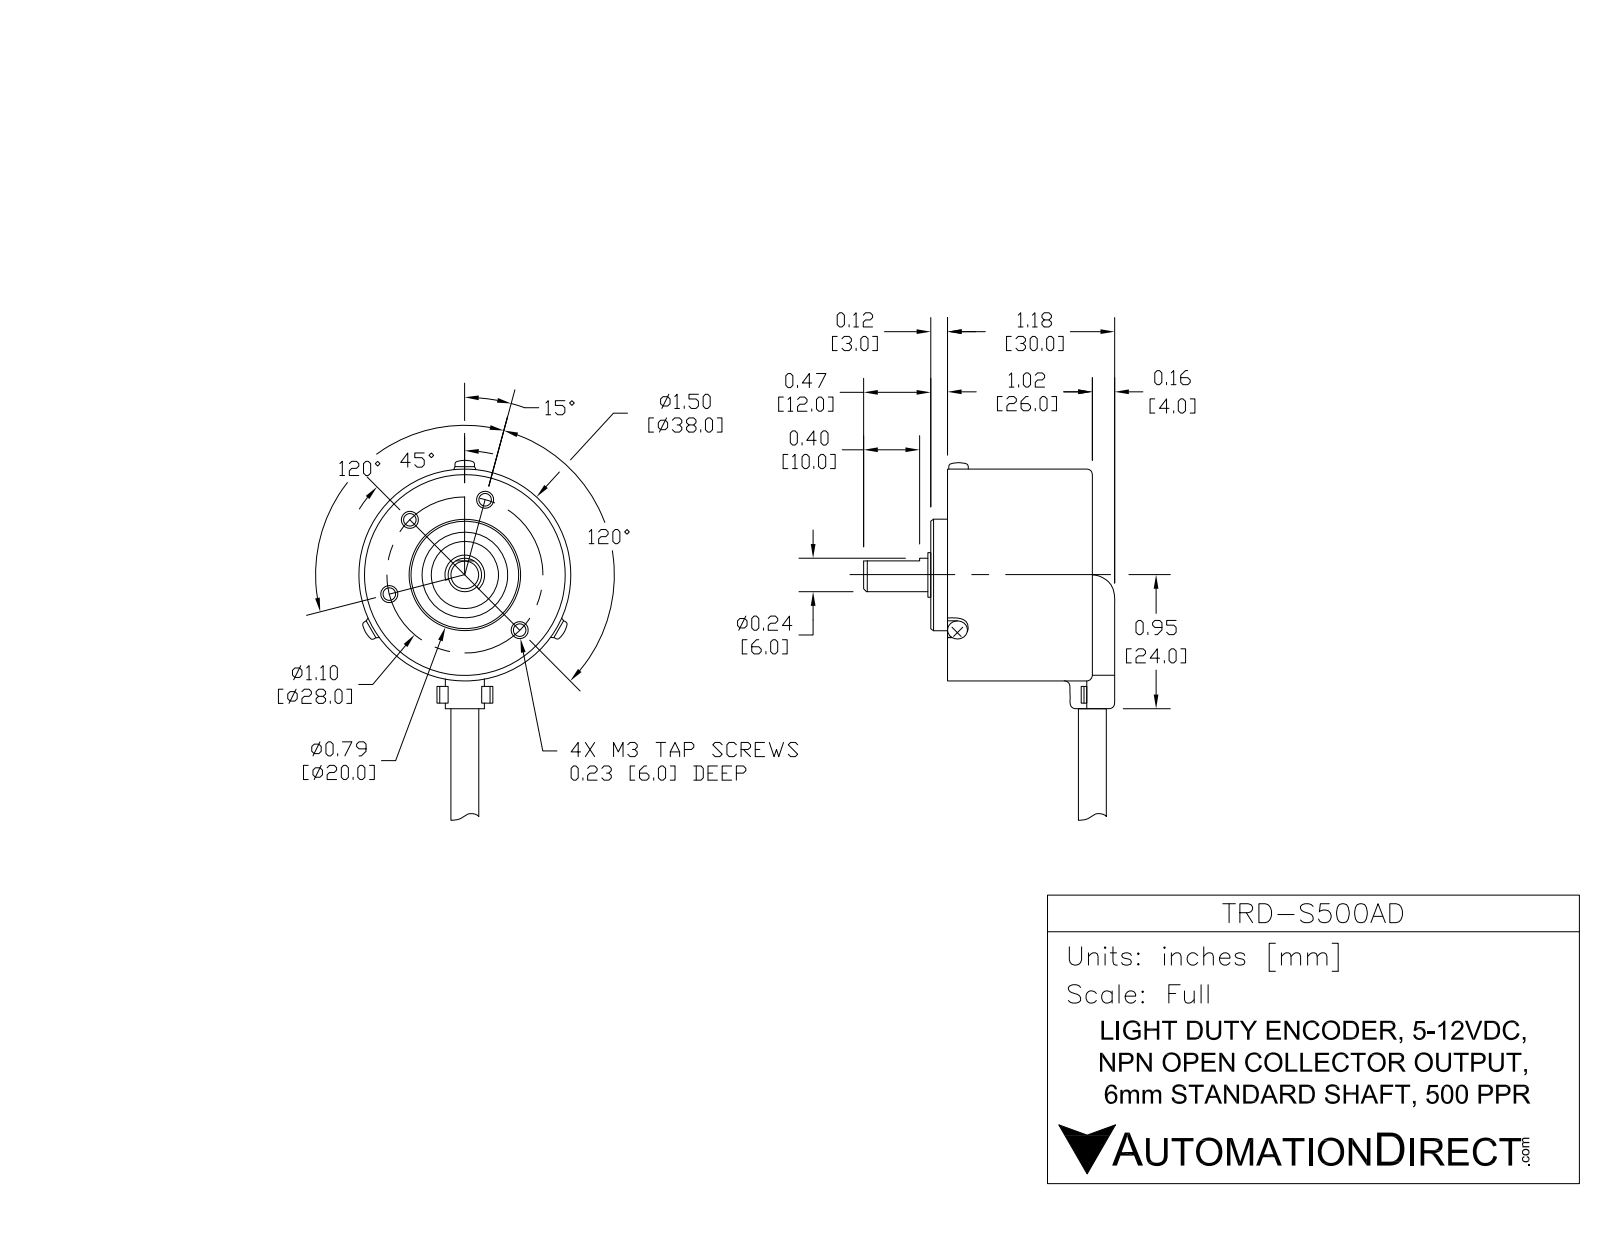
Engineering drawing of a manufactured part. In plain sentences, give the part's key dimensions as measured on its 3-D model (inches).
The part is named "TRD-S500AD". Its 3-D file was written by "SolidWorks 2016 (AUTOMOTIVE_DESIGN)". It is 3 solids with 257 faces: 98 planar, 100 cylindrical and 59 other. Overall it measures 7.189 by 1.768 by 1.496 inches. Its volume is 2.068 cubic inches and its surface area 13.85 square inches. Round holes: 4 of diameter 0.118, 1 of diameter 0.205, 1 of diameter 0.256, 1 of diameter 1.409. Round bosses or shafts: 1 of diameter 1.496, 1 of diameter 0.787, 1 of diameter 0.591, 1 of diameter 0.315, 1 of diameter 0.236, 1 of diameter 0.197, 1 of diameter 0.193. Partial cylindrical surfaces (rounded edges, fillets, slot ends): 11 of radius 0.016, 4 of radius 0.004, 3 of radius 0.13, 3 of radius 0.748, 2 of radius 0.008, 2 of radius 0.02, 2 of radius 0.146, 1 of radius 0.11. The main face-to-face distances are 1.024, 0.118, 1.142, 0.02, 0.138, 0.803, 1.161, 0.354, 0.335, 0.217. The hole center spacings are 0.551, 0.955, 0.954, 1.102.
